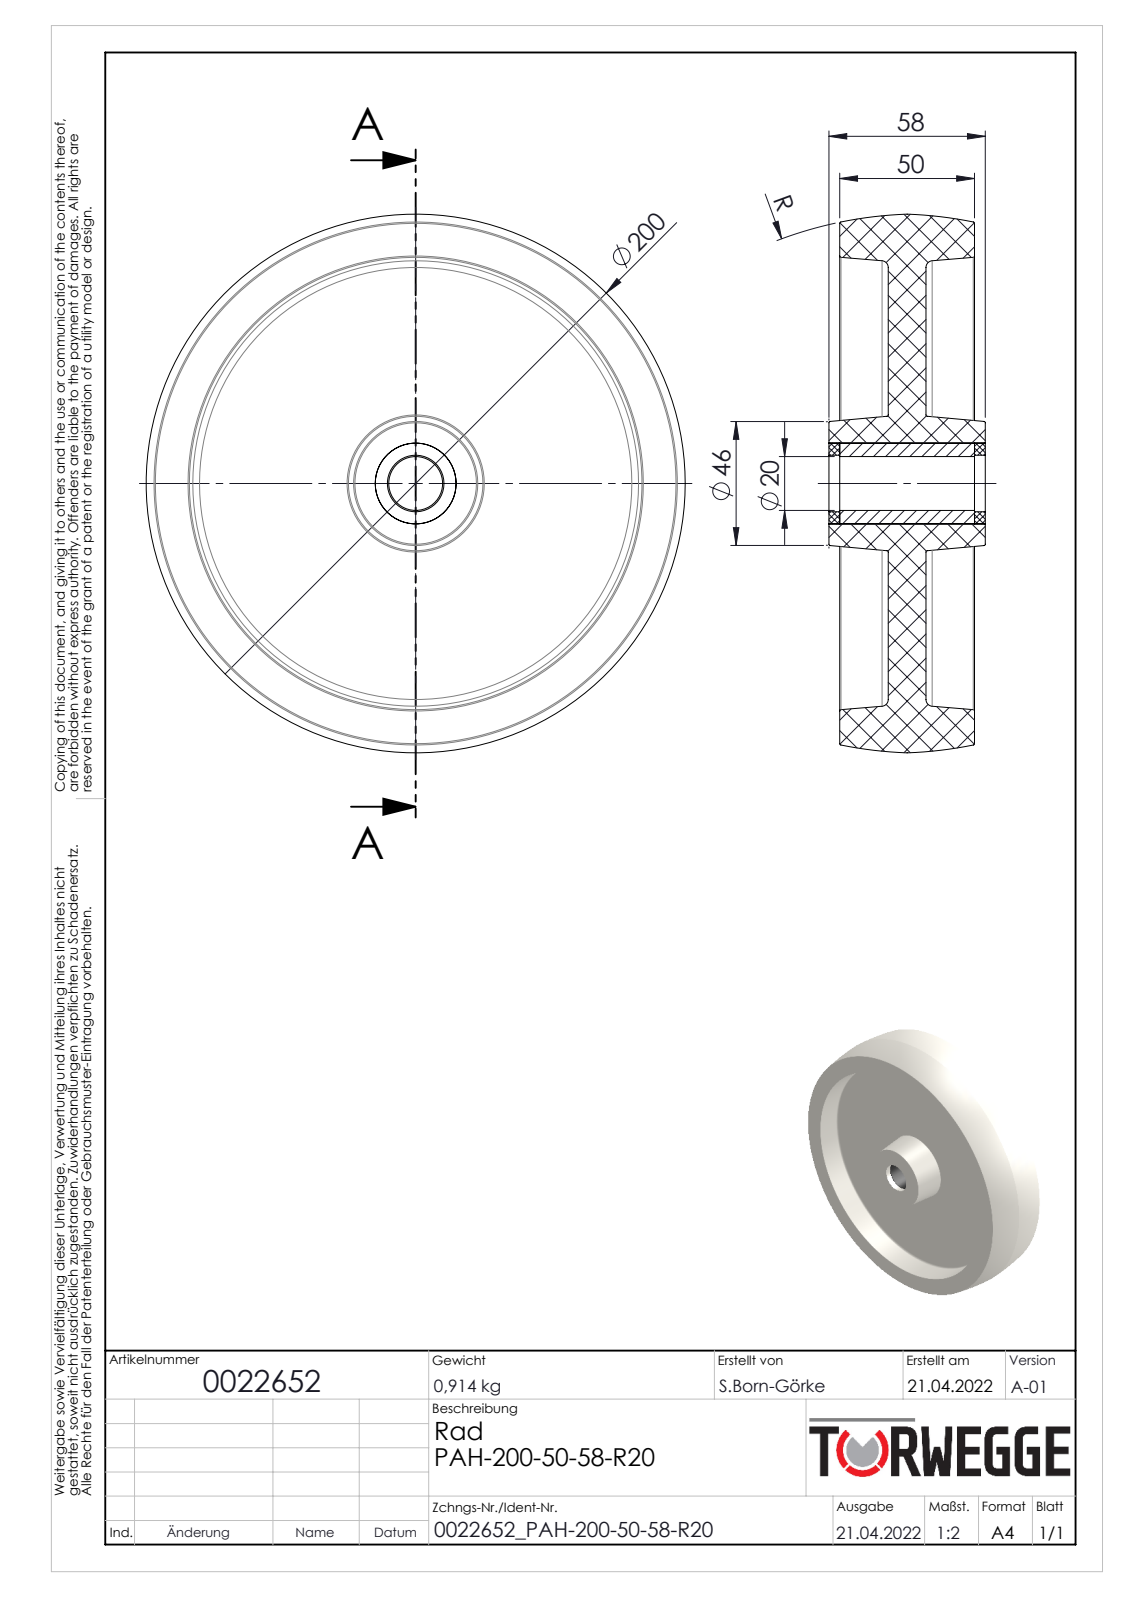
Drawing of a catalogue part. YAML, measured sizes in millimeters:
part_name: "0022652"
step_written_by: "SolidWorks 2020 (AUTOMOTIVE_DESIGN)"
units: millimeters
bodies: {solids: 4, faces: 58, planar: 12, cylindrical: 14, other: 32}
overall_size: [200, 200, 58]
volume: 813557
surface_area: 127865
round_holes:
  - {diameter: 20, count: 1}
  - {diameter: 21, count: 1}
round_bosses_or_shafts:
  - {diameter: 30, count: 1}
face_to_face_distances: [14, 18, 32, 50, 4, 22, 36, 54, 58]
